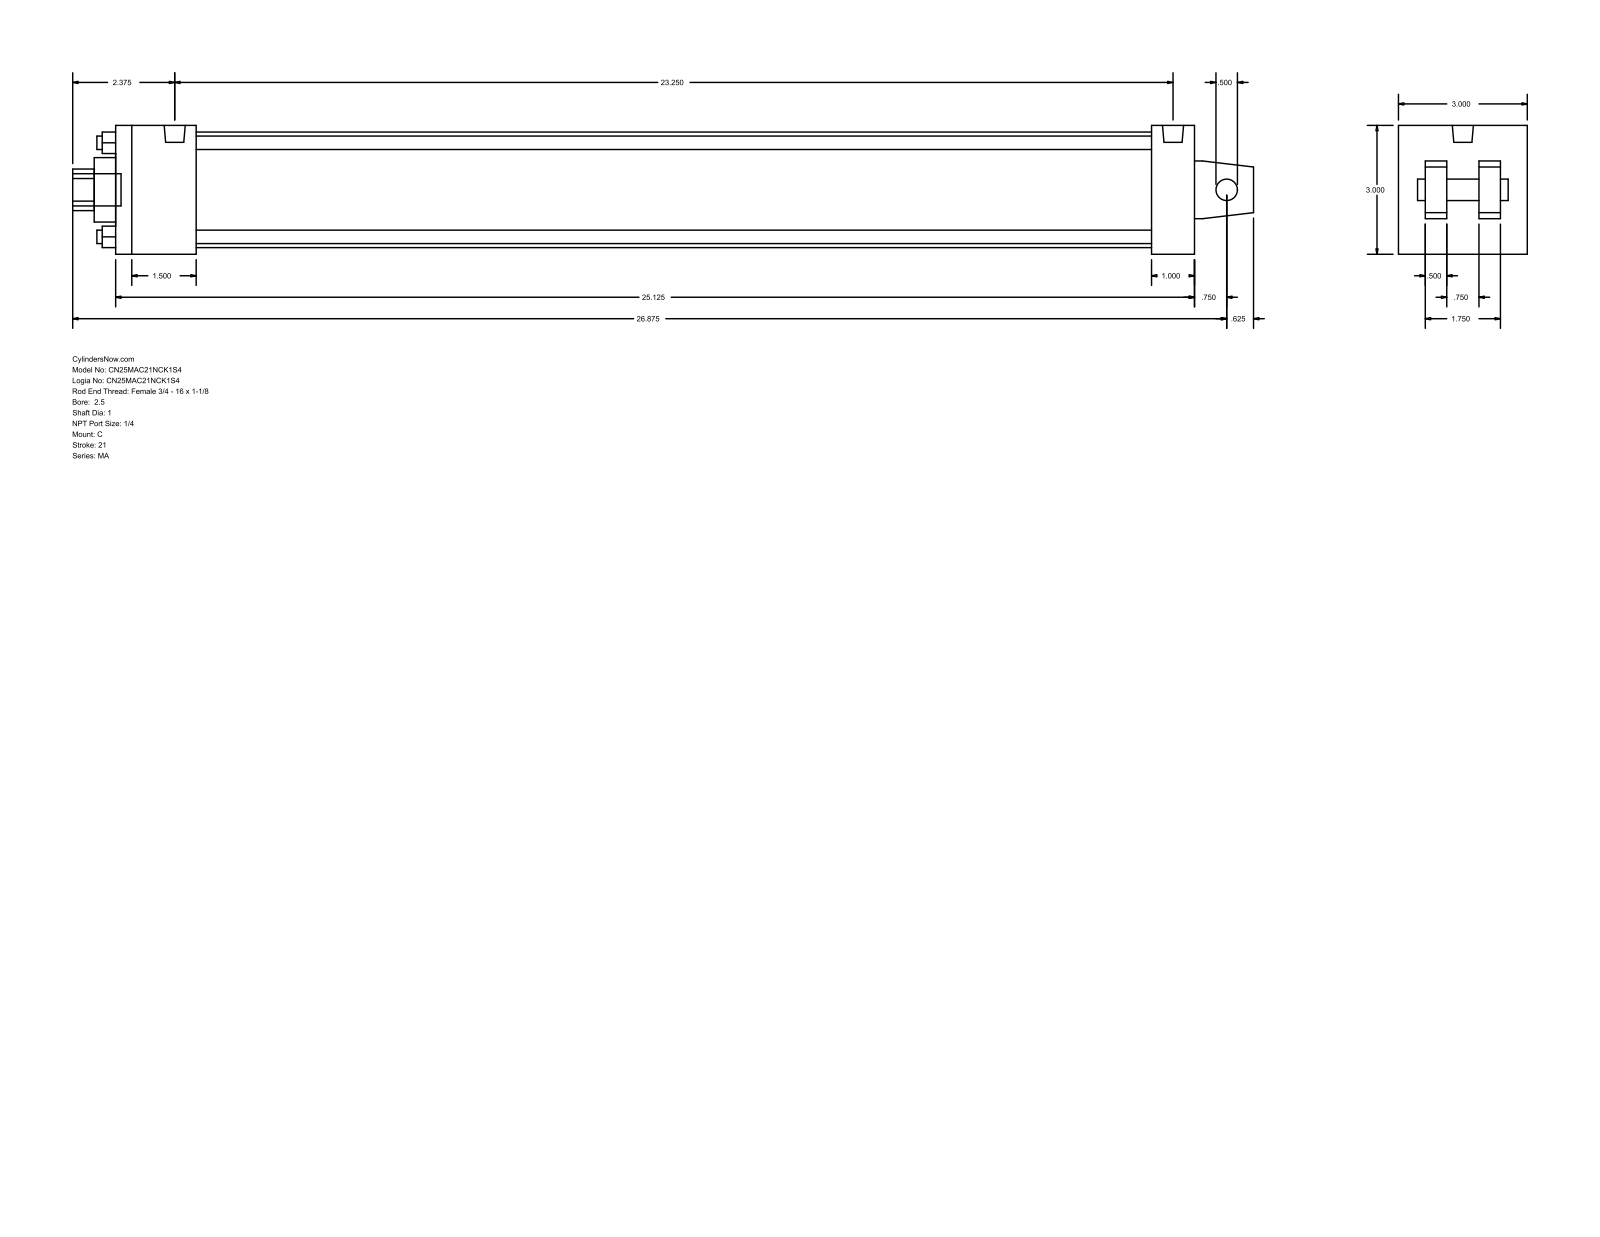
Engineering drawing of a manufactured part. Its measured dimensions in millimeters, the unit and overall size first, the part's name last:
Units: millimetres
Overall size (bounding box): 698.5 × 76.2 × 76.2
Round holes (diameter × count): ⌀7.94 ×4, ⌀12.7 ×1, ⌀25.4 ×1, ⌀38.1 ×1, ⌀68.33 ×1
Round bosses / shafts (diameter × count): ⌀7.94 ×4, ⌀12.49 ×2, ⌀19.05 ×1
Partial cylindrical surfaces — rounded edges, fillets, slot ends (radius × count): R12.29 ×1
Main face-to-face distances: 76.2, 47.63, 638.18, 12.7, 60.33, 15.87, 28.57, 612.77, 565.14, 590.55
Hole centre spacings: 39.33, 55.62, 78.66
Bodies: 0 solids, 103 faces (76 planar, 27 cylindrical, 0 other)
Part name (STEP PRODUCT): MA_C__0250_1
STEP written by: GSSL Pune (CONFIG_CONTROL_DESIGN)
